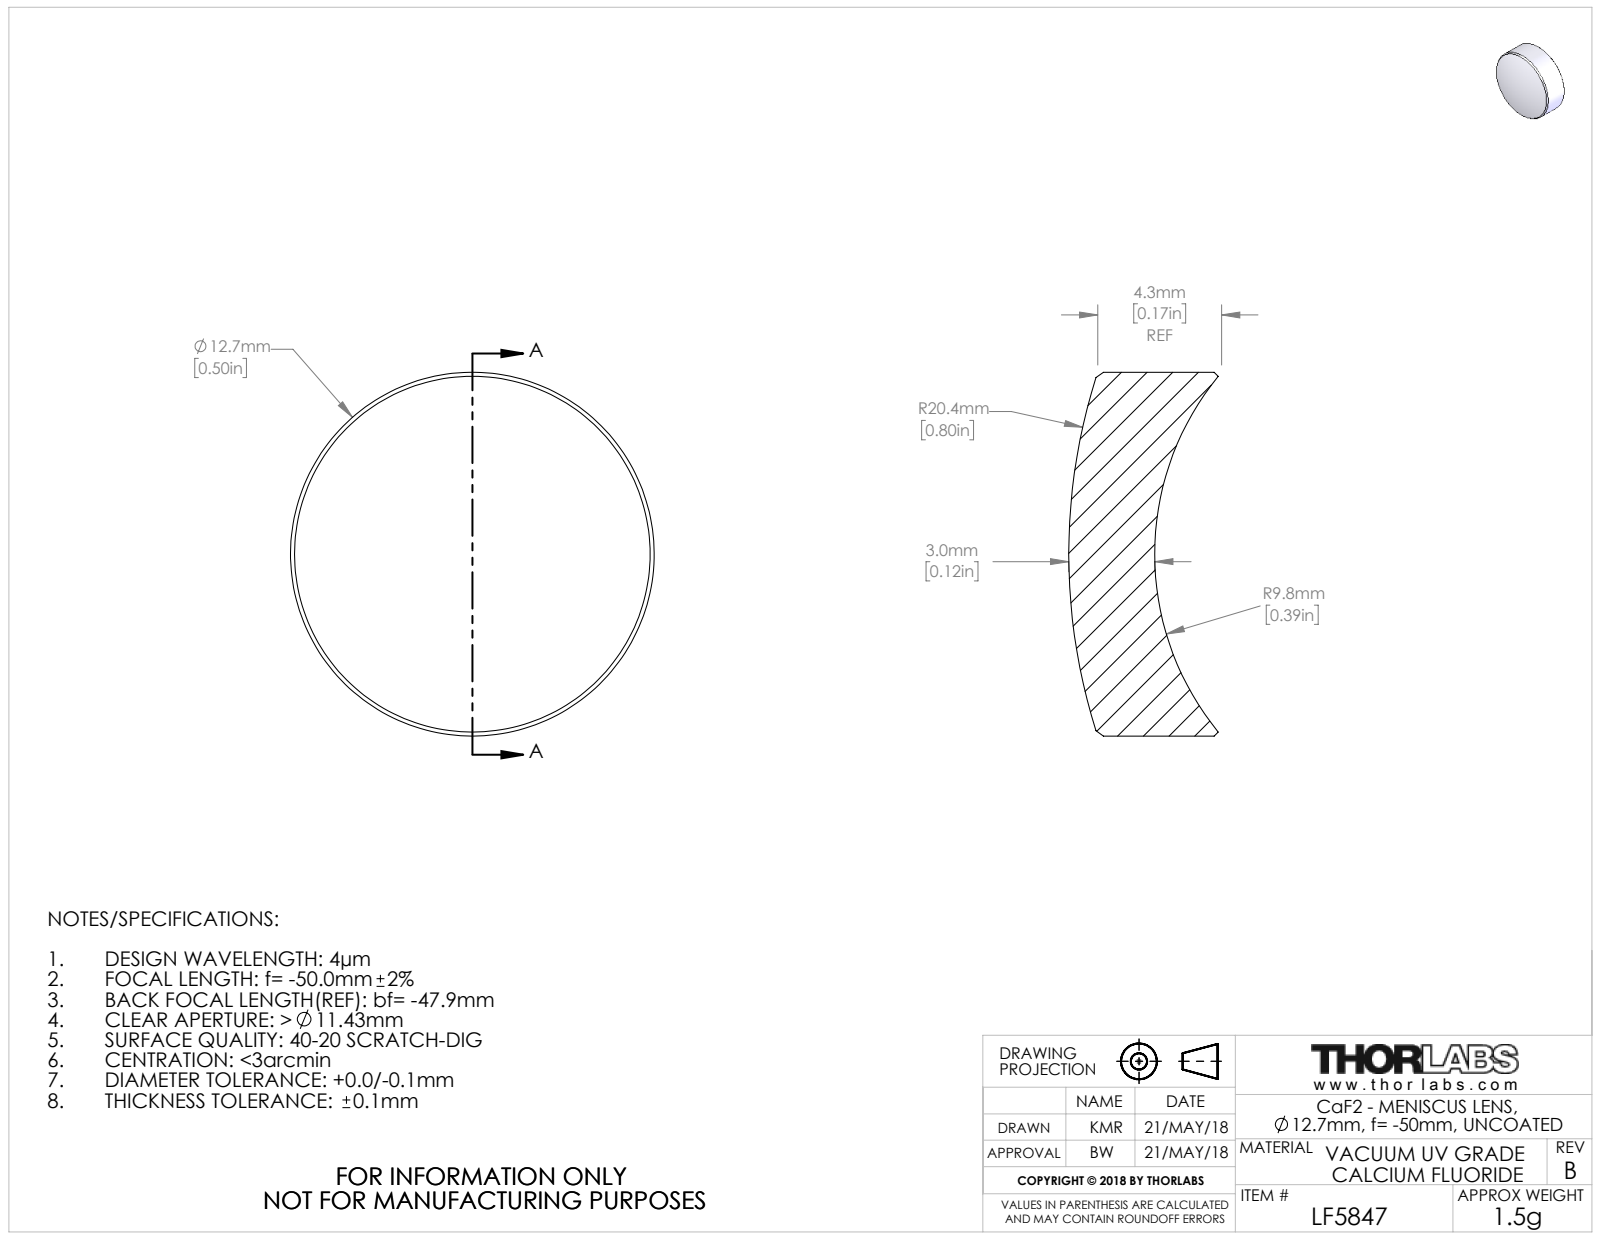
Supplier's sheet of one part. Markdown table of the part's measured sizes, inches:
| quantity | value |
| --- | --- |
| part name | 21996-E0W |
| STEP written by | SolidWorks 2016 (CONFIG_CONTROL_DESIGN) |
| units | inches |
| bodies | 1 solid, 10 faces (0 planar, 2 cylindrical, 8 other) |
| overall size | 0.5 × 0.5 × 0.206 |
| volume | 0.028 in³ |
| surface area | 0.672 in² |
| round bosses / shafts (diameter × count) | 0.5 × 1 |
